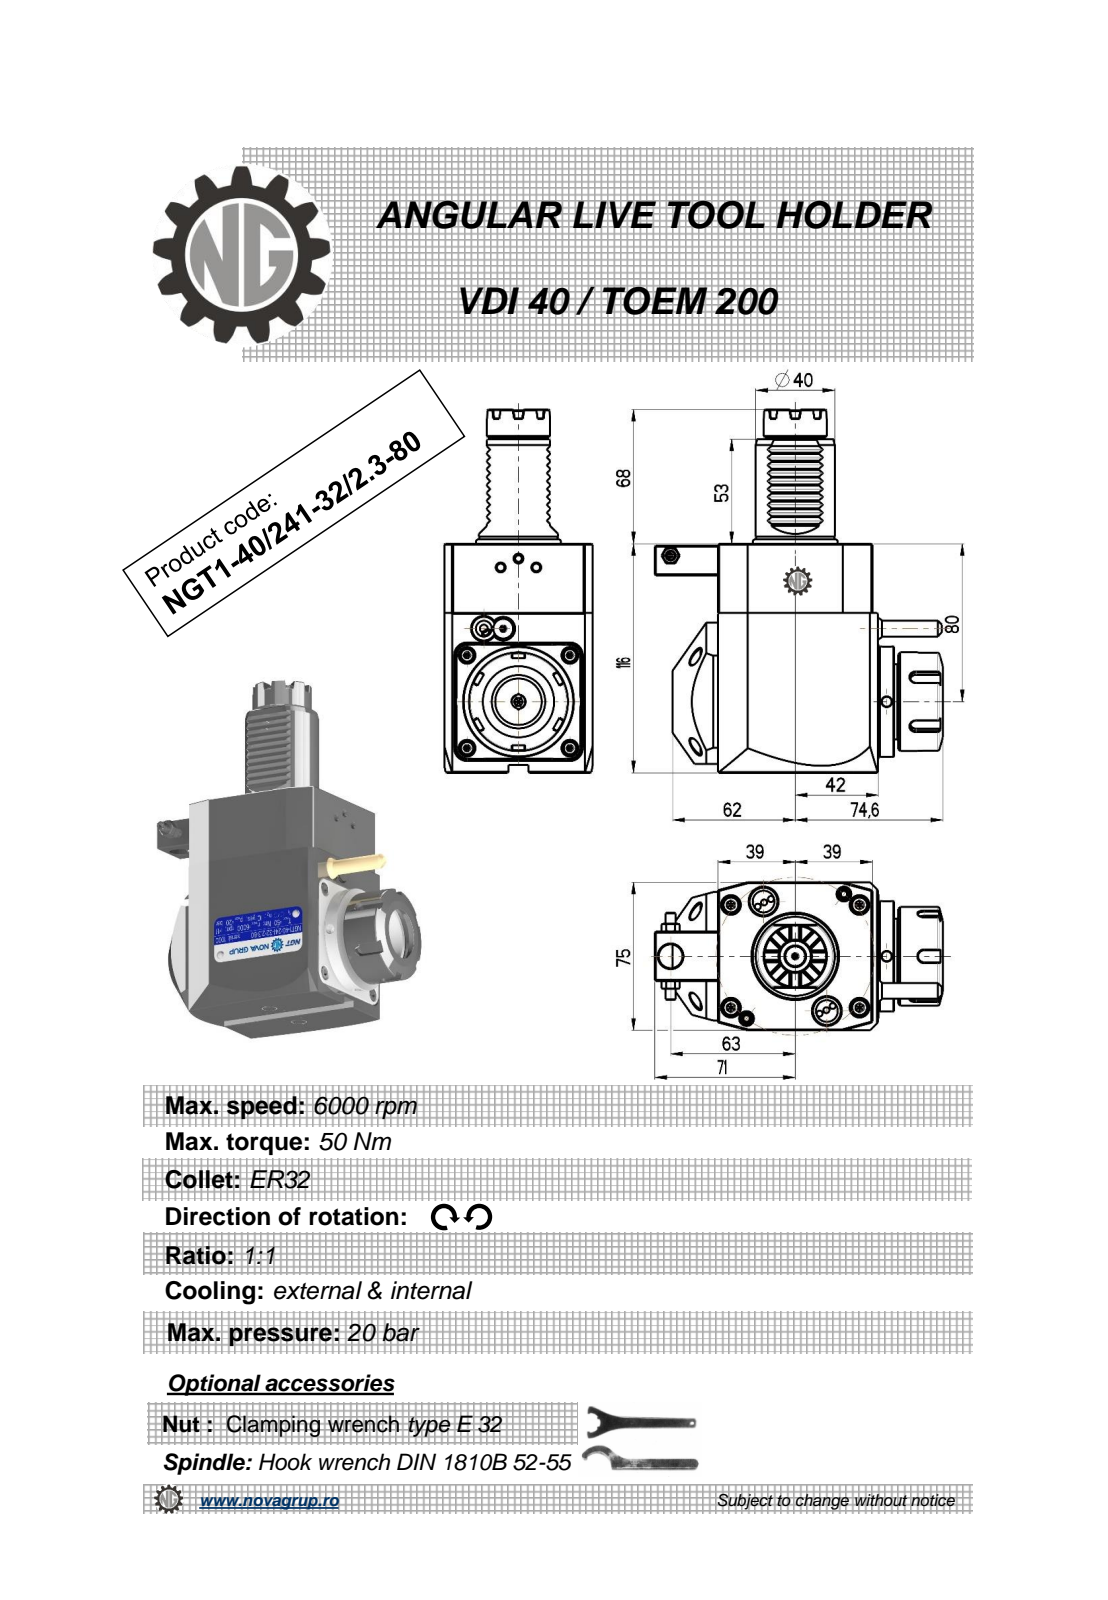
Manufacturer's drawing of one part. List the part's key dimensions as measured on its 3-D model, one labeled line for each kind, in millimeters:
Part name (STEP PRODUCT): NGT1_40_241_32_2_3_80
STEP written by: PRO/ENGINEER BY PARAMETRIC TECHNOLOGY CORPORATION, 2010280 (CONFIG_CONTROL_DESIGN)
Units: millimetres
Bodies: 1 solid, 535 faces (263 planar, 94 cylindrical, 178 other)
Overall size (bounding box): 184 × 145.6 × 75
Volume: 890 004 mm³ · Surface area: 73 059 mm²
Round holes (diameter × count): ⌀5 ×3, ⌀3 ×1, ⌀4.2 ×1, ⌀9.5 ×1, ⌀12 ×1, ⌀27 ×1
Round bosses / shafts (diameter × count): ⌀56 ×1, ⌀50 ×1, ⌀43 ×1, ⌀40 ×1, ⌀32 ×1, ⌀17.2 ×1, ⌀10 ×1, ⌀8.96 ×1
Partial cylindrical surfaces — rounded edges, fillets, slot ends (radius × count): R0.3 ×20, R0.26 ×12, R0.2 ×6, R3 ×5, R40 ×1
Main face-to-face distances: 75, 116, 78, 81, 3, 112, 80.8, 2.8, 7.5, 0.5
Hole centre spacings: 39.58, 40.93, 72.5, 109.25, 131.95
